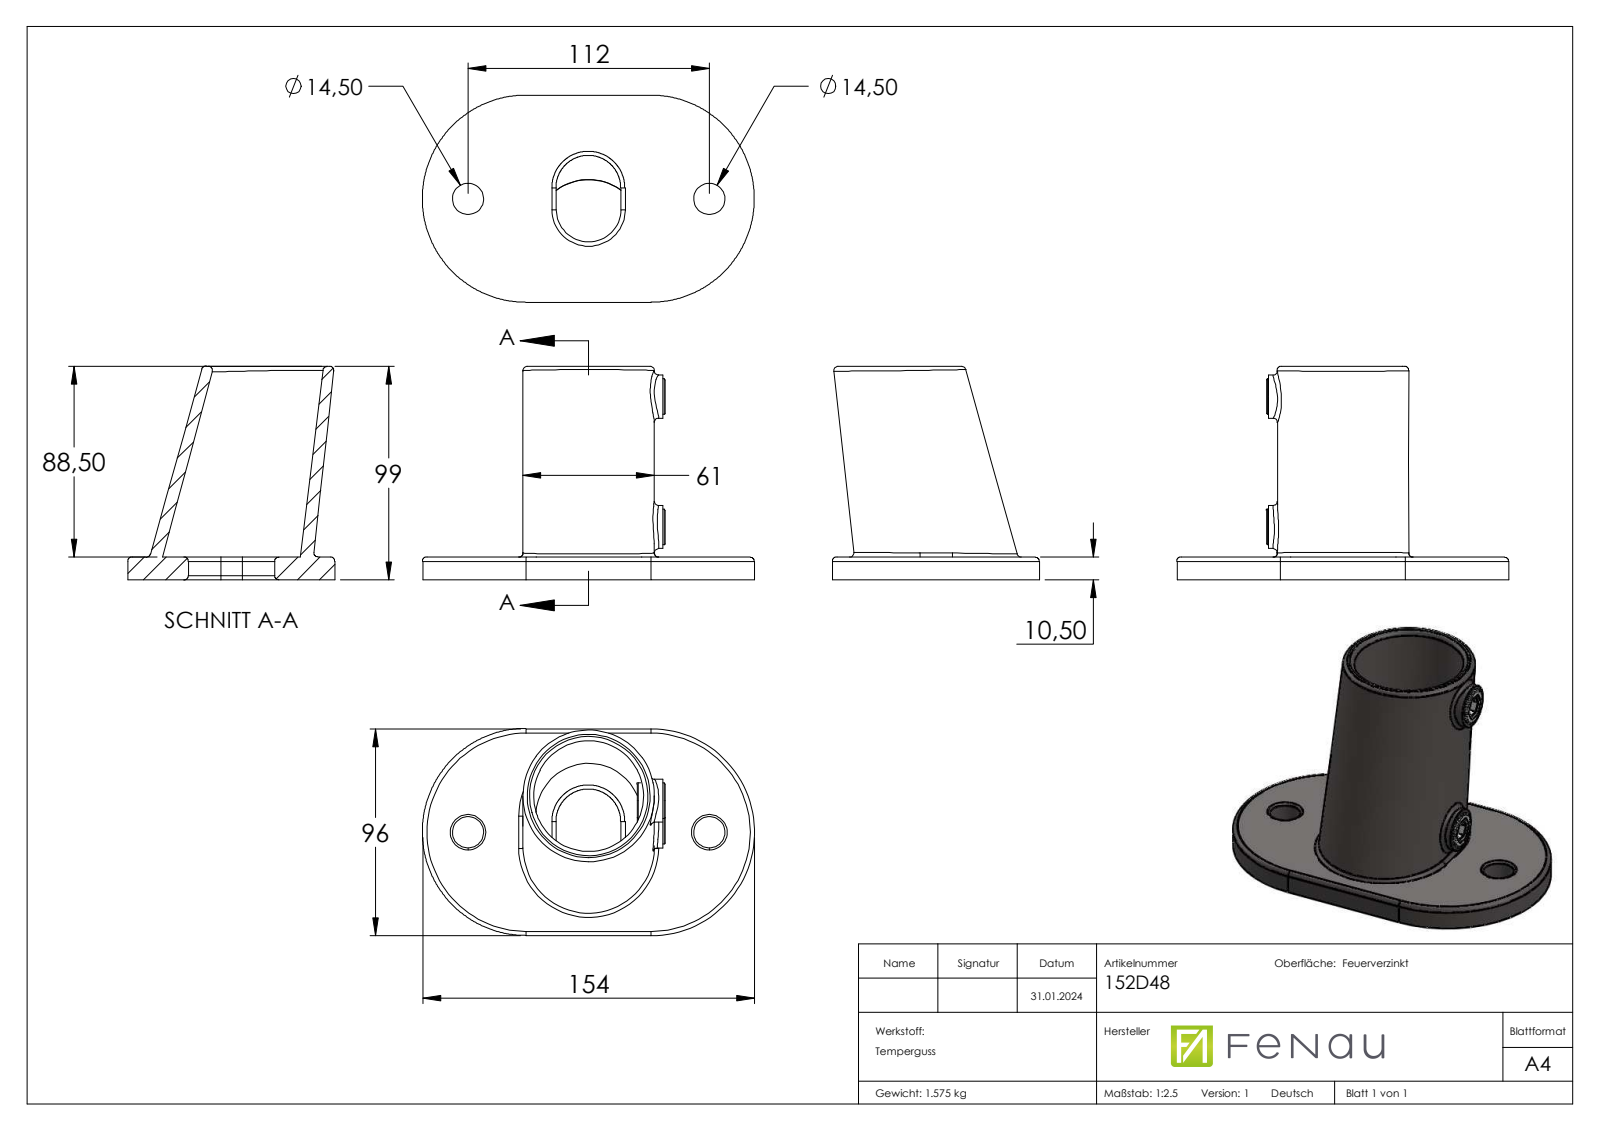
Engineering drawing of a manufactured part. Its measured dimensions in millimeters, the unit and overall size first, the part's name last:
Units: millimetres
Overall size (bounding box): 154 × 99 × 96
Round holes (diameter × count): ⌀14.5 ×2, ⌀15.25 ×2
Round bosses / shafts (diameter × count): ⌀20 ×2, ⌀16.5 ×2
Partial cylindrical surfaces — rounded edges, fillets, slot ends (radius × count): R2 ×30, R15 ×2, R48 ×2
Main face-to-face distances: 10.5, 96, 8.1, 12, 13, 1, 99, 88.5, 9.95, 78.55
Hole centre spacings: 61.66, 112
Volume: 215 587 mm³ · Surface area: 65 145 mm²
Bodies: 3 solids, 91 faces (26 planar, 42 cylindrical, 23 other)
Part name (STEP PRODUCT): 152-D48 Teil2_152-D48 Teil2; 152-D48 Teil1_152-D48 Teil1; 152-D48
STEP written by: SolidWorks 2018 (CONFIG_CONTROL_DESIGN)
